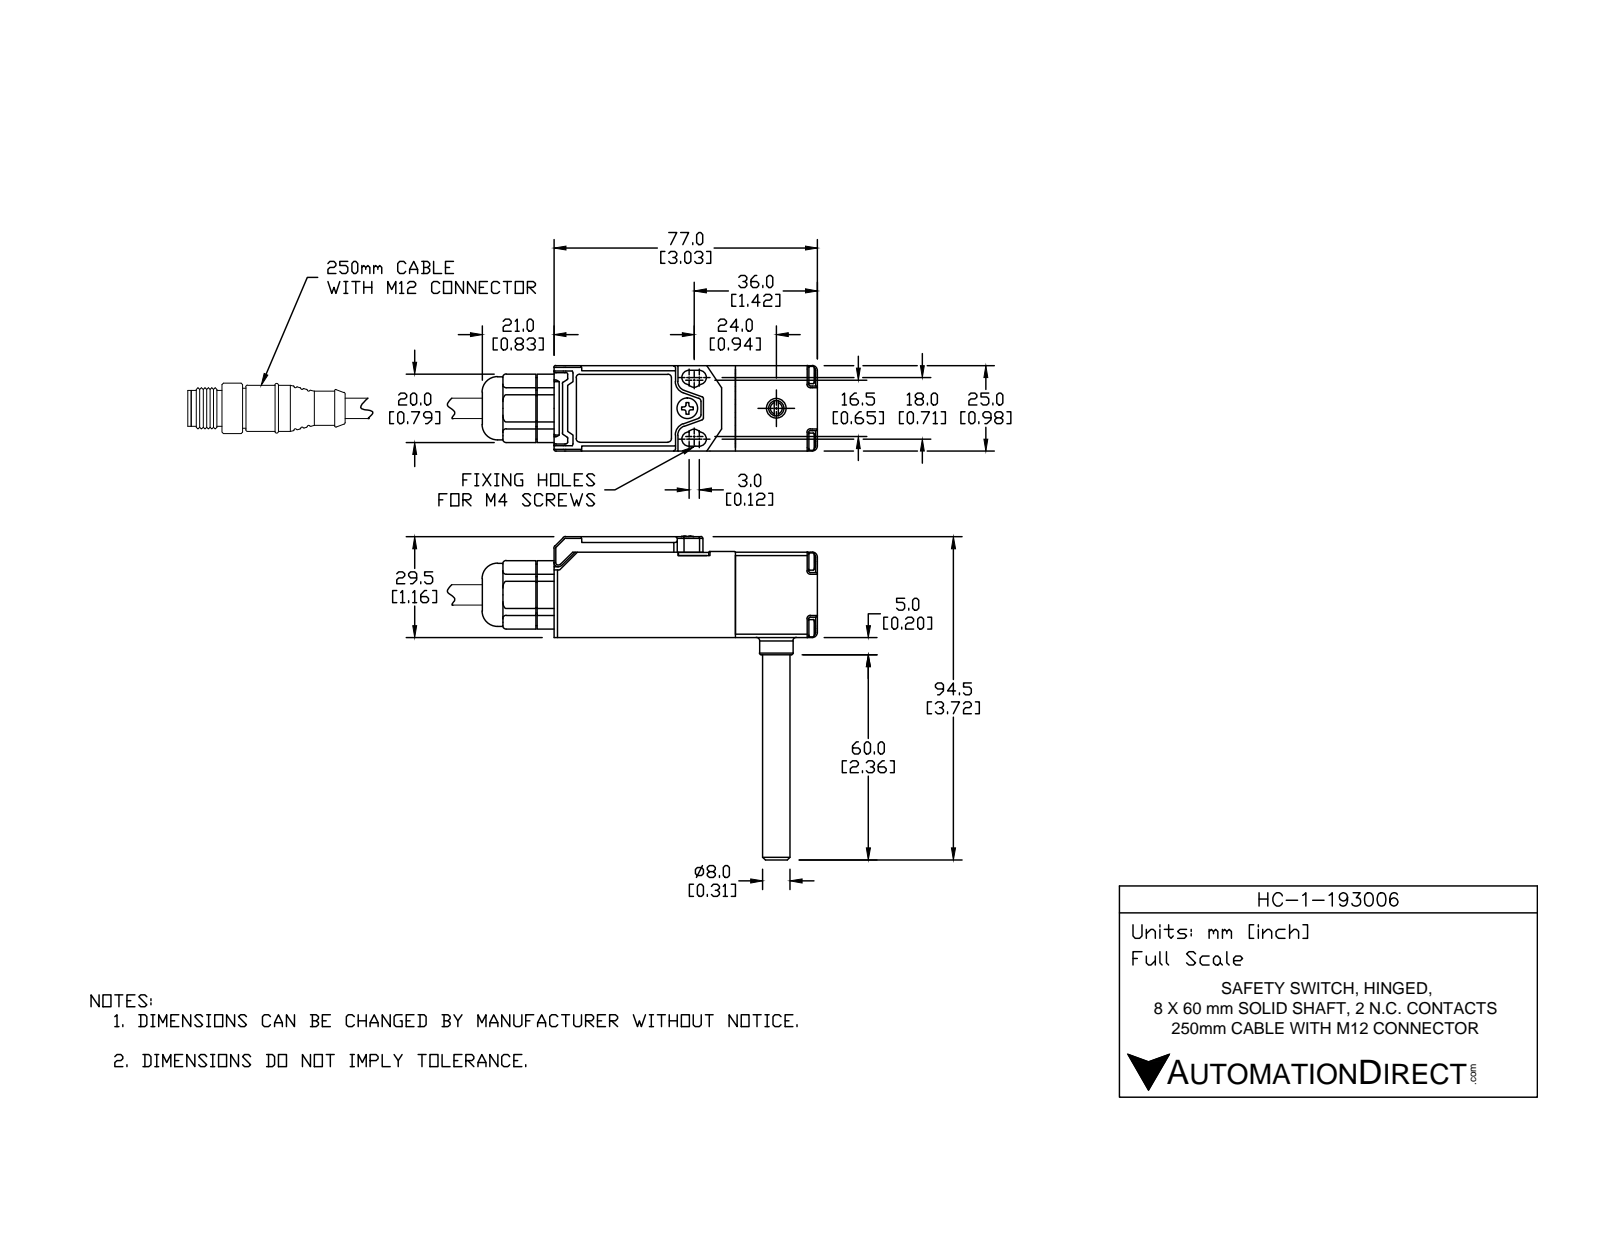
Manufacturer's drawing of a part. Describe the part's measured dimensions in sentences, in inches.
The part is named "HC-1-193006". Its 3-D file was written by "SolidWorks 2014 (AUTOMOTIVE_DESIGN)". It is 14 solids with 1702 faces: 700 planar, 601 cylindrical and 401 other. Overall it measures 3.73 by 3.169 by 0.984 inches. Its volume is 1.733 cubic inches and its surface area 42.86 square inches. Round holes: 5 of diameter 0.126, 4 of diameter 0.094, 2 of diameter 0.059, 2 of diameter 0.063, 2 of diameter 0.071, 2 of diameter 0.087, 2 of diameter 0.142, 1 of diameter 0.055, 1 of diameter 0.081, 1 of diameter 0.098, 1 of diameter 0.102, 1 of diameter 0.185. Round bosses or shafts: 5 of diameter 0.102, 4 of diameter 0.197, 4 of diameter 0.079, 2 of diameter 0.138, 1 of diameter 0.74, 1 of diameter 0.531, 1 of diameter 0.386, 1 of diameter 0.315. Partial cylindrical surfaces (rounded edges, fillets, slot ends): 226 of radius 0.02, 24 of radius 0.004, 20 of radius 0.012, 20 of radius 0.039, 7 of radius 0.059, 6 of radius 0.083, 6 of radius 0.11, 4 of radius 0.008. The main face-to-face distances are 0.984, 0.079, 0.071, 0.913, 0.039, 0.906, 0.945, 0.827, 0.874, 1.15. The hole center spacings are 0.543, 0.768, 0.171, 0.187, 0.245, 0.414, 0.423, 0.426.
